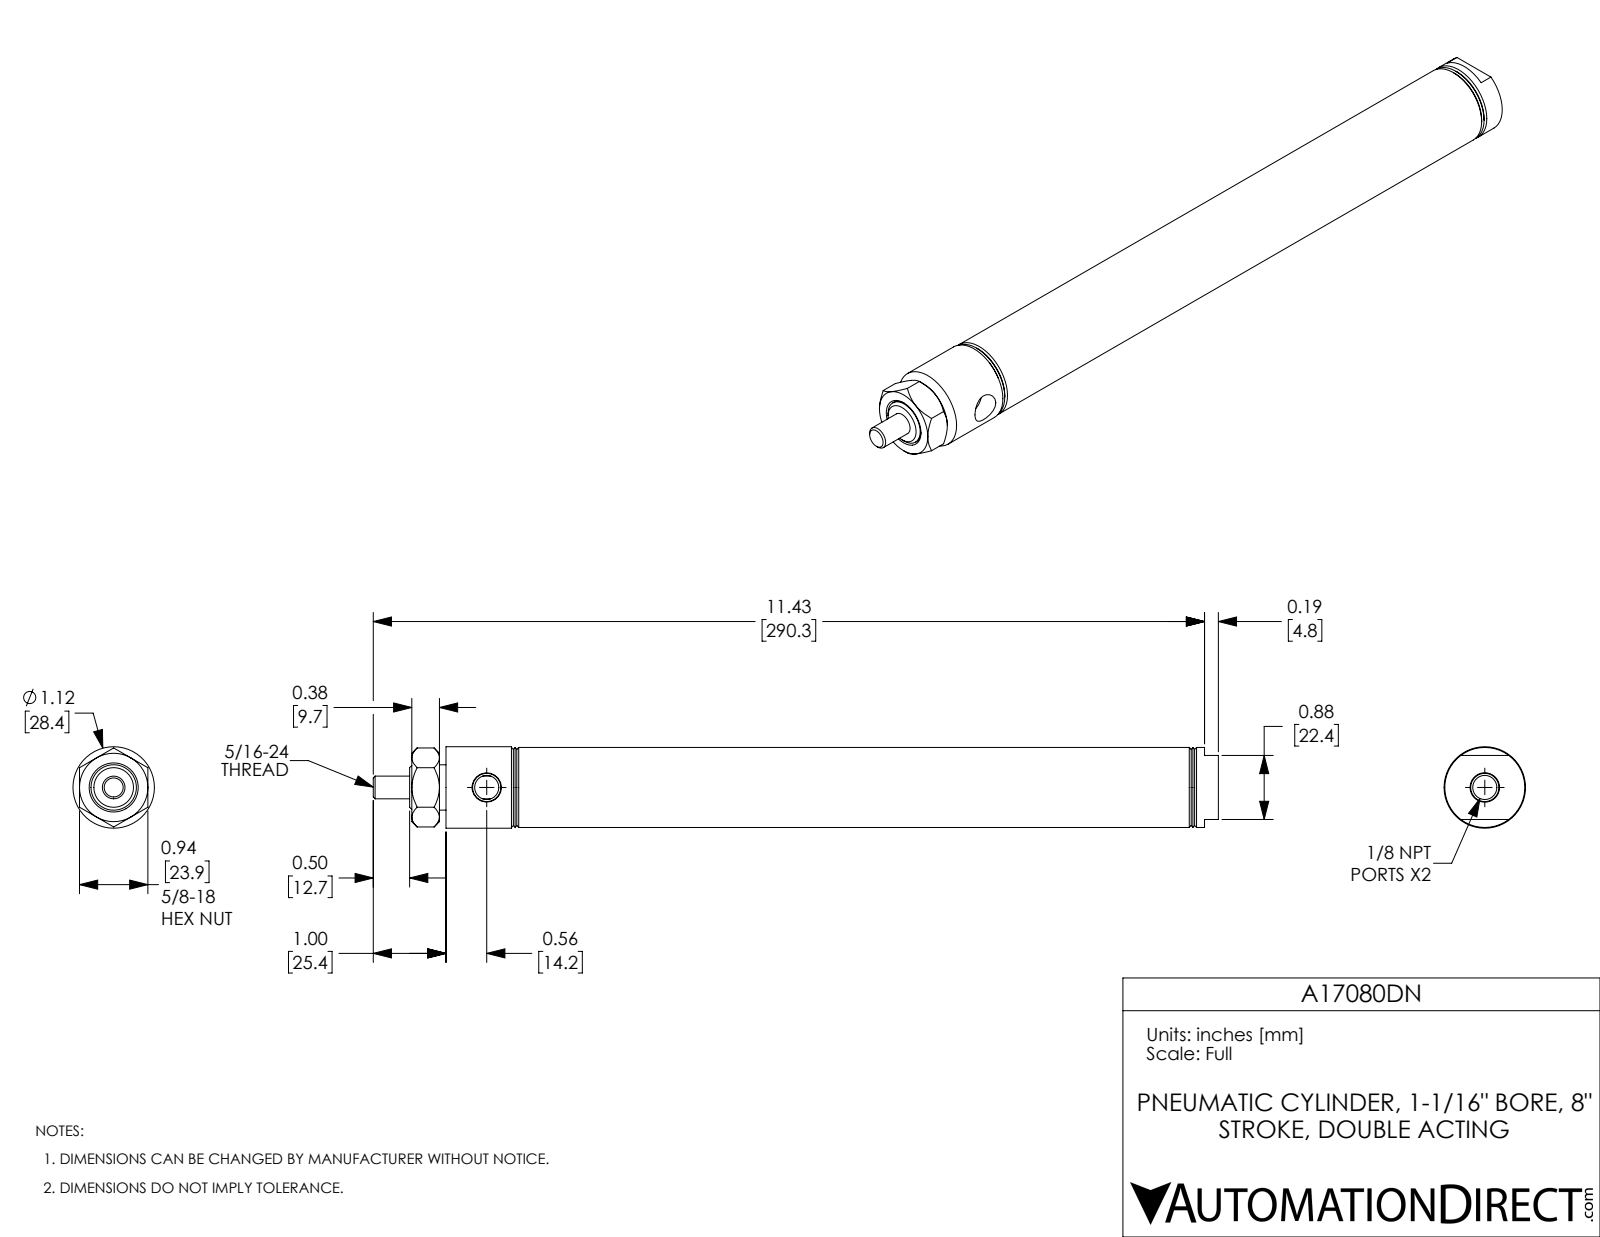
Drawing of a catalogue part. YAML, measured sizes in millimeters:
part_name: "A17080DN-MainBody; A17080DN-Rod; A17080DN_Mounting Nut_D-9; A17080DN"
step_written_by: "SolidWorks 2017 (AUTOMOTIVE_DESIGN)"
units: millimeters
bodies: {solids: 3, faces: 94, planar: 24, cylindrical: 26, other: 44}
overall_size: [295.1, 28.4, 28.4]
volume: 62940
surface_area: 57230
round_holes:
  - {diameter: 8.4, count: 2}
  - {diameter: 7.9, count: 1}
  - {diameter: 15.9, count: 1}
  - {diameter: 27, count: 1}
round_bosses_or_shafts:
  - {diameter: 28.4, count: 1}
  - {diameter: 27.9, count: 1}
  - {diameter: 15.8, count: 1}
face_to_face_distances: [12.7, 242.8, 215.9, 203.2, 26.9, 39.6, 242.8, 269.7, 230.1, 26.9]
